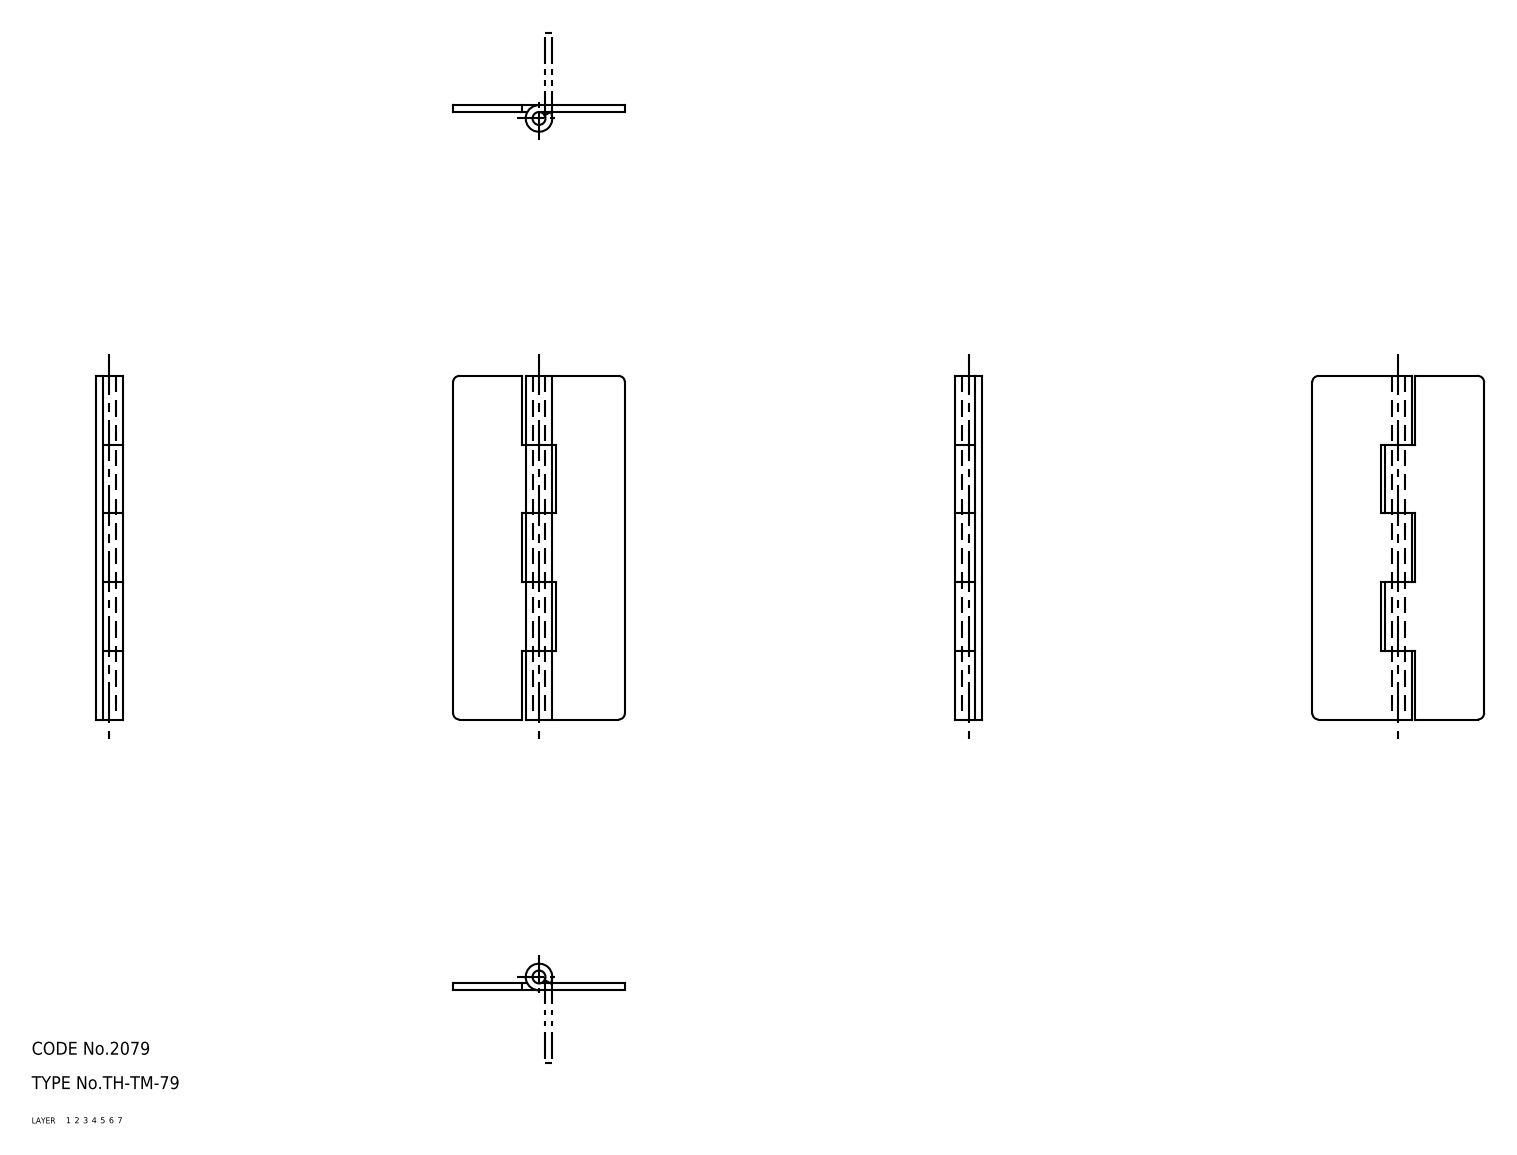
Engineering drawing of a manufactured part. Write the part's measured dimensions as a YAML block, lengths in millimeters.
part_name: "67111201; 67111214; 67111227"
step_written_by: "CADfix (AUTOMOTIVE_DESIGN)"
units: millimeters
bodies: {solids: 3, faces: 46, planar: 0, cylindrical: 0, other: 46}
overall_size: [80, 40, 6.2]
volume: 6702
surface_area: 9304
